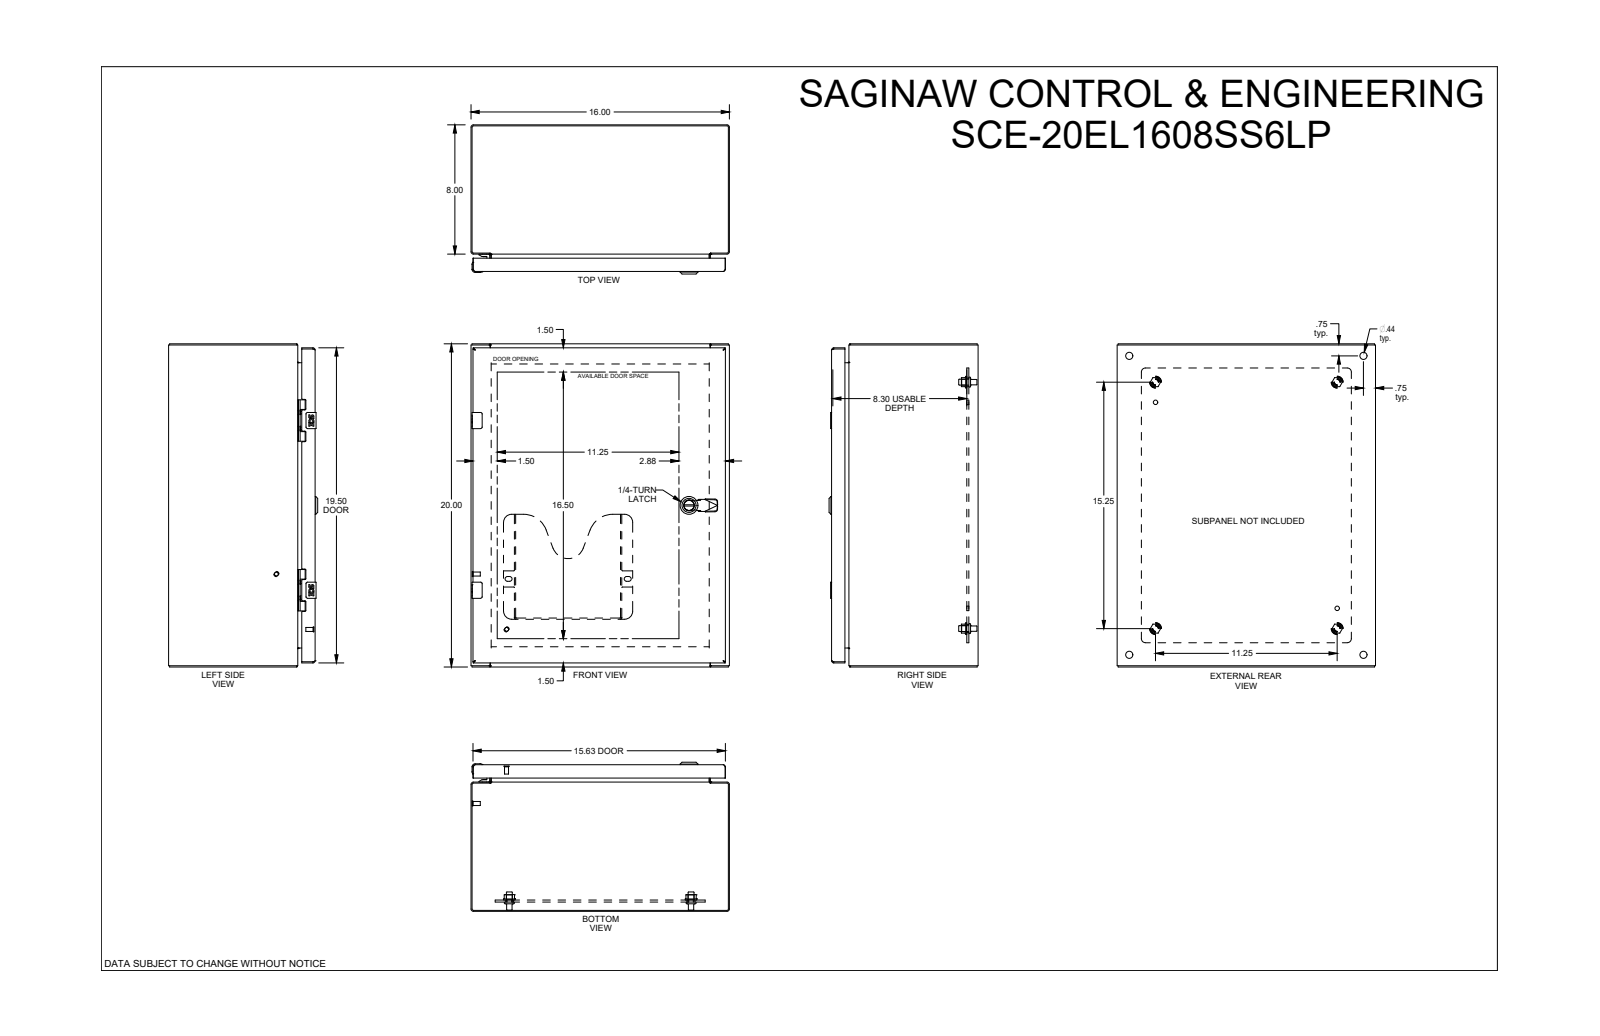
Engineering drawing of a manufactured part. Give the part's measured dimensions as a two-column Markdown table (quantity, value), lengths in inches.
| quantity | value |
| --- | --- |
| part name | SCE-20EL1608LP |
| STEP written by | SolidWorks 2021 (AUTOMOTIVE_DESIGN) |
| units | inches |
| bodies | 24 solids, 1217 faces (544 planar, 474 cylindrical, 199 other) |
| overall size | 20 × 16 × 9.935 |
| volume | 143.9 in³ |
| surface area | 3 503 in² |
| round holes (diameter × count) | 0.172 × 4, 0.205 × 4, 0.244 × 4, 0.375 × 4, 0.437 × 4, 0.5 × 4, 0.04 × 2, 0.188 × 2, 0.218 × 2, 0.281 × 2, 0.197 × 1, 0.204 × 1 |
| round bosses / shafts (diameter × count) | 0.375 × 4, 0.33 × 4, 0.25 × 4, 0.248 × 4, 0.24 × 4, 1.102 × 1, 0.78 × 1, 0.63 × 1 |
| partial cylindrical surfaces (radius × count) | 0.015 × 24, 0.04 × 17, 0.22 × 16, 0.043 × 12, 0.118 × 12, 0.031 × 10, 0.06 × 9, 0.062 × 8 |
| main face-to-face distances | 0.075, 0.06, 8.993, 15.925, 9.068, 9.008, 8.933, 19.925, 0.575, 0.5 |
| hole center spacings | 0.494, 10.5, 0.984, 1.25, 2.317, 2.319, 2.452, 2.87 |
